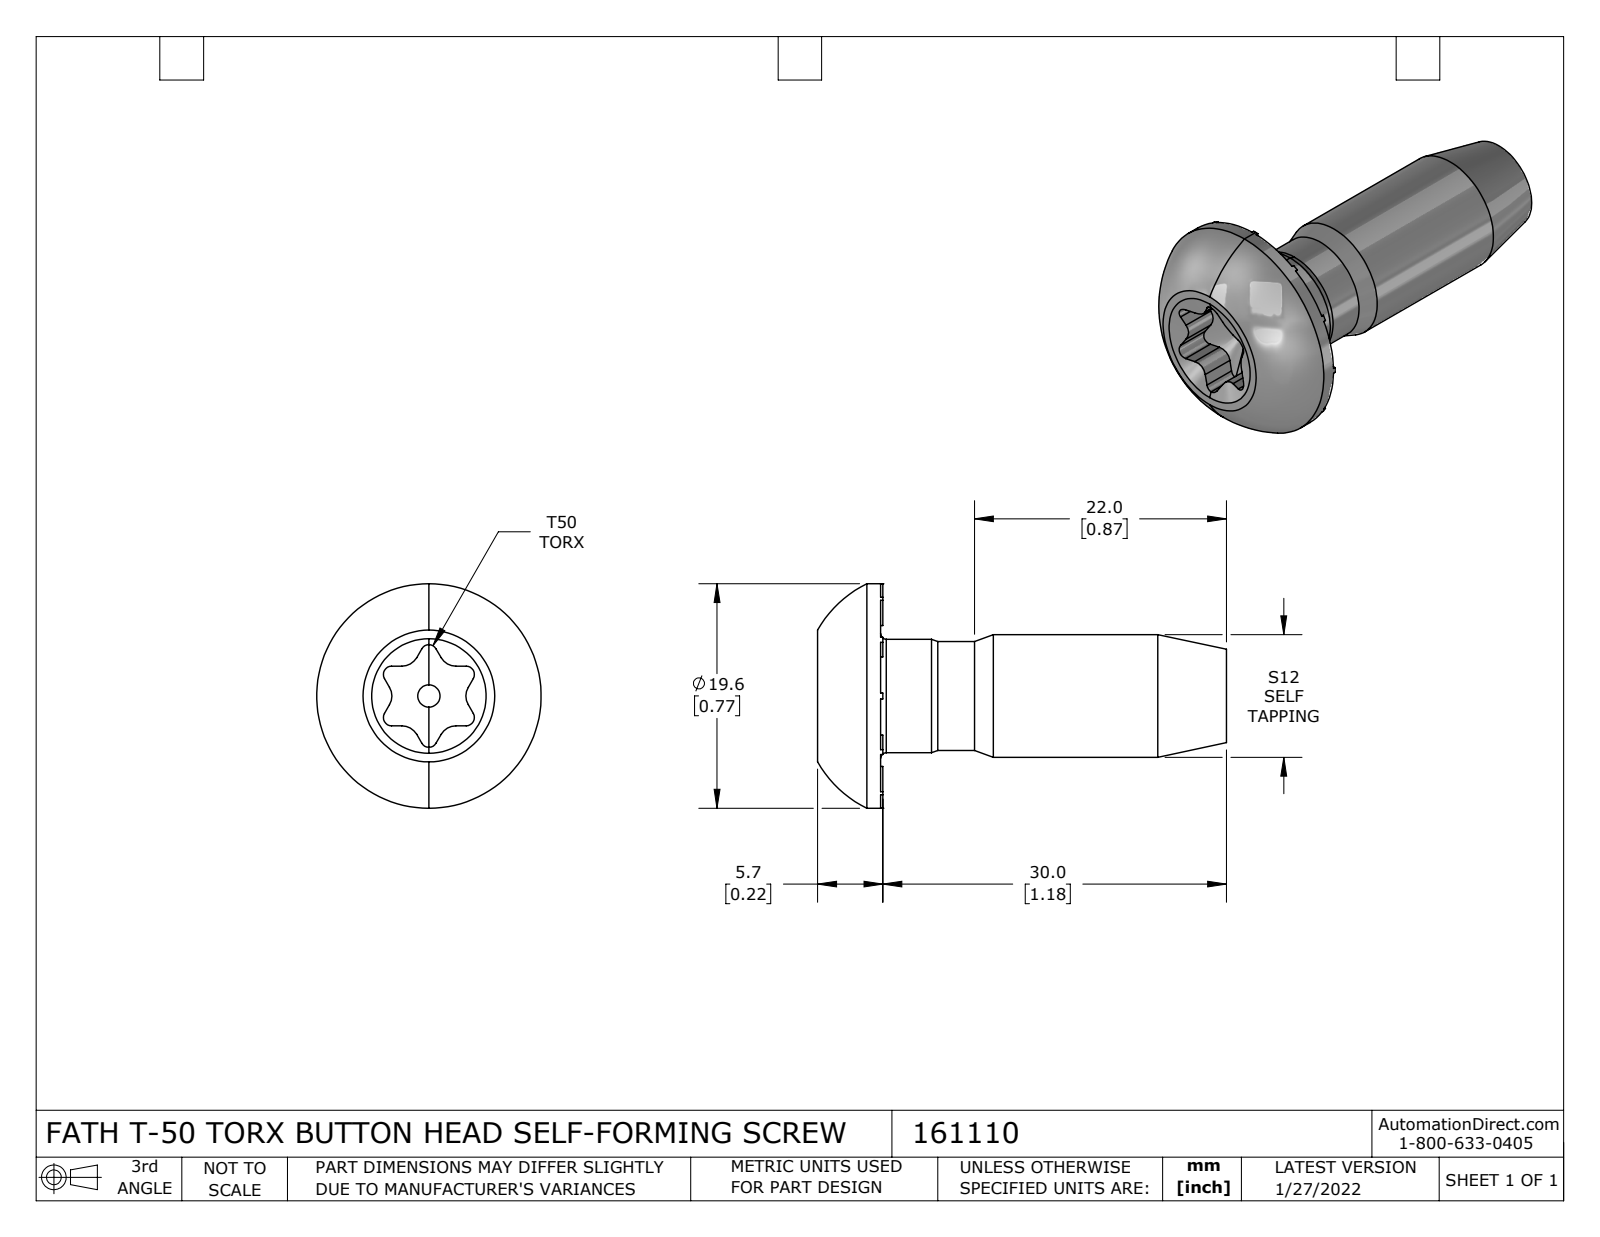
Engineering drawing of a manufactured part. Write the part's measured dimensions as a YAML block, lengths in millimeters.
part_name: "161110"
step_written_by: "SolidWorks 2021 (CONFIG_CONTROL_DESIGN)"
units: millimeters
bodies: {solids: 1, faces: 100, planar: 52, cylindrical: 34, other: 14}
overall_size: [35.7, 19.6, 19.6]
volume: 3558
surface_area: 1829
round_bosses_or_shafts:
  - {diameter: 19.6, count: 1}
  - {diameter: 10.7, count: 1}
  - {diameter: 9.9, count: 1}
  - {diameter: 9.5, count: 1}
partial_cylinders:
  - {radius: 0.72, count: 6}
  - {radius: 1.5, count: 6}
  - {radius: 7.25, count: 1}
face_to_face_distances: [30.2, 35.7, 5.5, 5.2, 30, 5.7, 2.35, 2.85, 0.5, 31.2]
